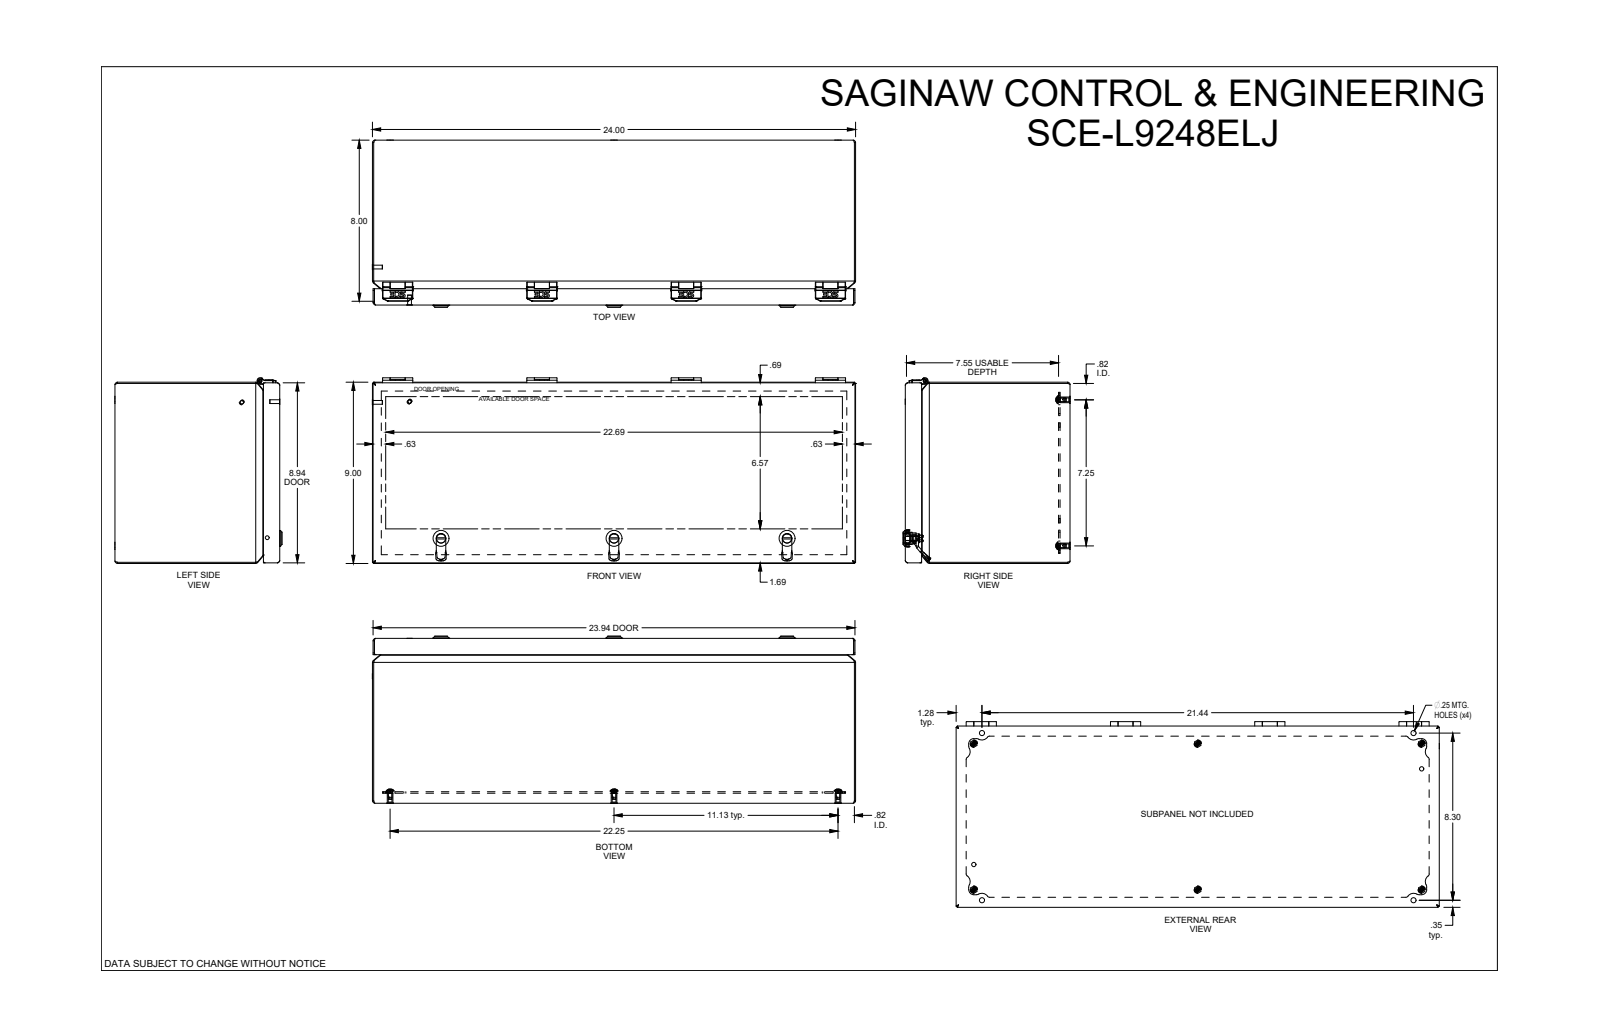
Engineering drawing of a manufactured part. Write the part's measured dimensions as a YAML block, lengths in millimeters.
part_name: "SCE-L9248ELJ"
step_written_by: "SolidWorks 2021 (AUTOMOTIVE_DESIGN)"
units: millimeters
bodies: {solids: 56, faces: 2433, planar: 1239, cylindrical: 604, other: 590}
overall_size: [609.7, 234.2, 210.7]
volume: 1316000
surface_area: 1625000
round_holes:
  - {diameter: 4.8, count: 6}
  - {diameter: 6.4, count: 6}
  - {diameter: 7.2, count: 6}
  - {diameter: 4.2, count: 4}
  - {diameter: 4.4, count: 4}
  - {diameter: 8.6, count: 4}
  - {diameter: 5.1, count: 3}
  - {diameter: 6.1, count: 3}
  - {diameter: 6.5, count: 3}
  - {diameter: 6.8, count: 3}
  - {diameter: 7.2, count: 3}
  - {diameter: 8.3, count: 3}
round_bosses_or_shafts:
  - {diameter: 4.8, count: 8}
  - {diameter: 9.5, count: 6}
  - {diameter: 7.1, count: 6}
  - {diameter: 6.6, count: 4}
  - {diameter: 3.8, count: 4}
  - {diameter: 20, count: 3}
  - {diameter: 13.9, count: 3}
  - {diameter: 11.7, count: 3}
partial_cylinders:
  - {radius: 0.2, count: 64}
  - {radius: 0.5, count: 42}
  - {radius: 0.3, count: 18}
  - {radius: 1.3, count: 16}
  - {radius: 3.2, count: 13}
  - {radius: 6.4, count: 13}
  - {radius: 1.6, count: 10}
  - {radius: 0.8, count: 9}
face_to_face_distances: [1.5, 227.1, 1.6, 207.9, 206.4, 206.3, 204.8, 14.5, 13, 191.8]
hole_center_spacings: [182, 282.6, 364.1, 182, 184.2, 184.2, 337.3, 337.3]
